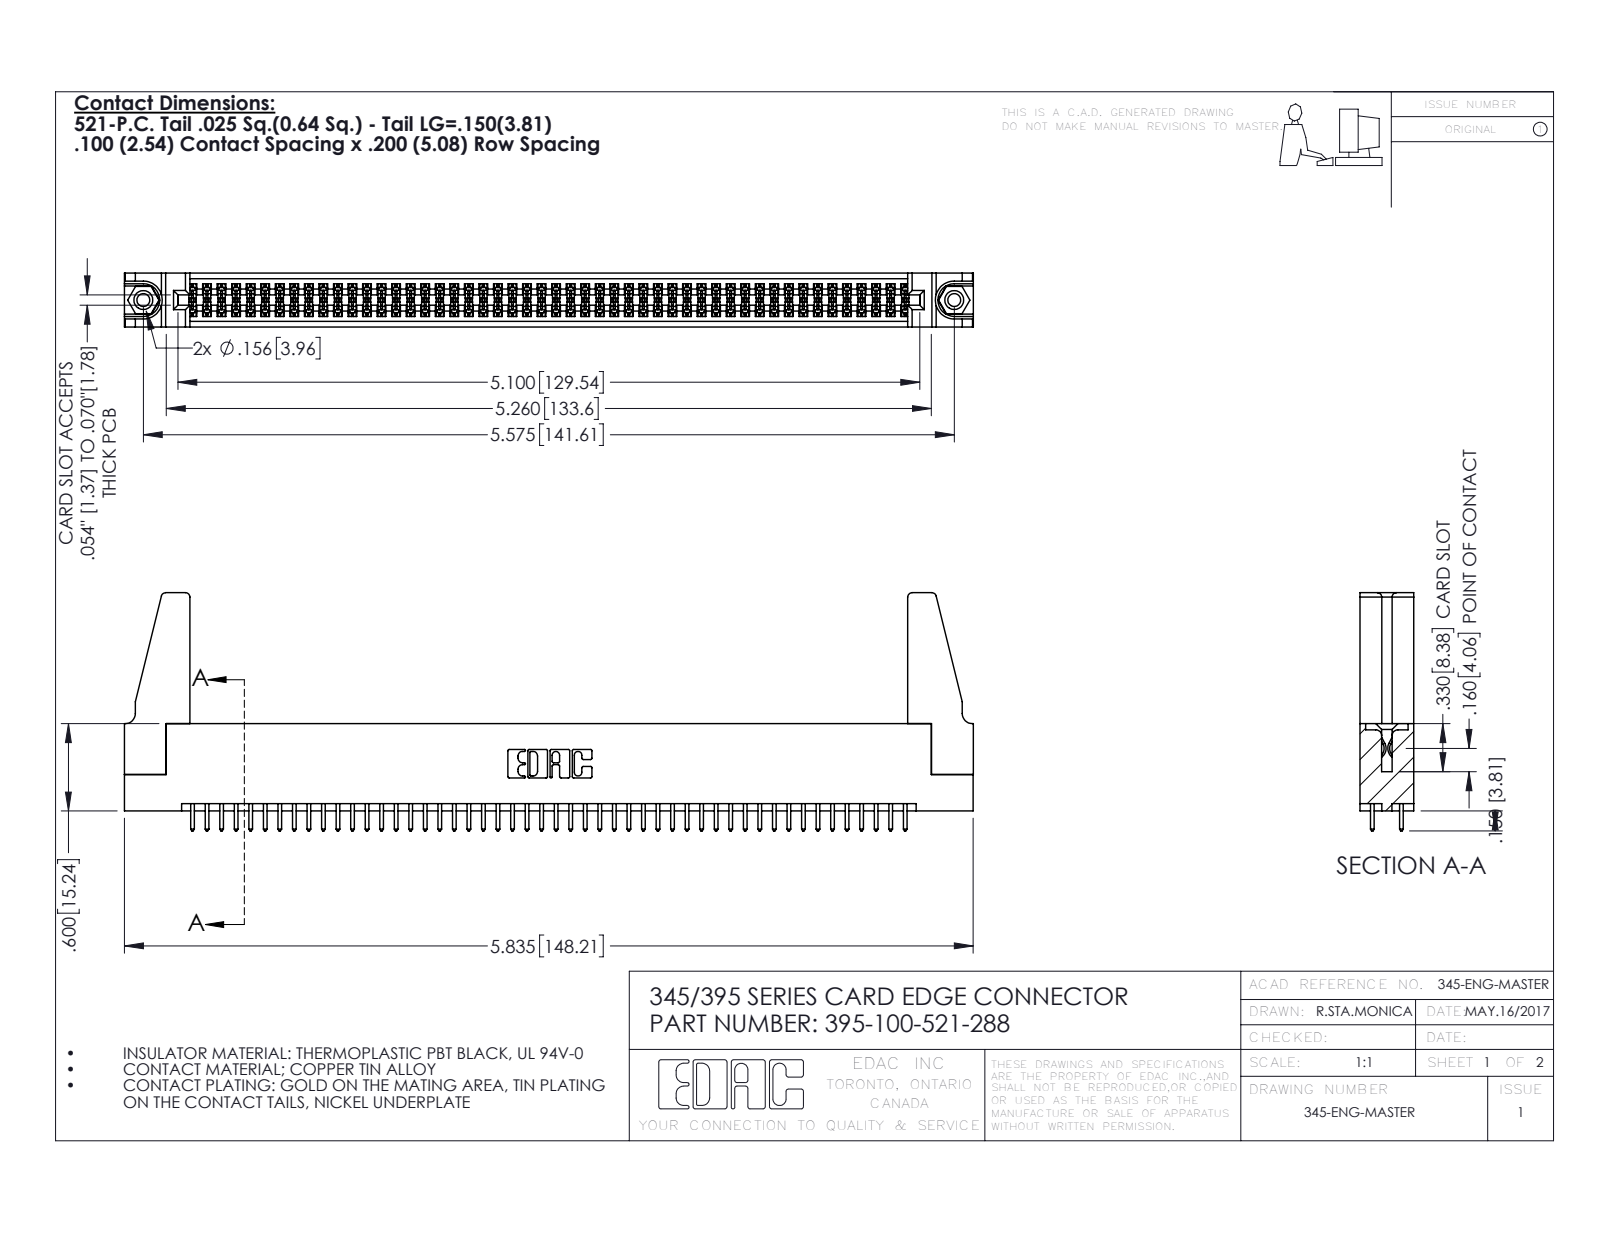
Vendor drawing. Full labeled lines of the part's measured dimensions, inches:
Part name (STEP PRODUCT): 345-220-078_345-220-088; 345 Part_Flush Mounting Lugs - 0.156 Dia-TH; 395-100-521-288; 345-250-001_345-250-001-102 (+1 more)
STEP written by: SolidWorks 2016 (CONFIG_CONTROL_DESIGN)
Units: inches
Bodies: 105 solids, 5250 faces (3452 planar, 1782 cylindrical, 16 other)
Overall size (bounding box): 5.836 × 1.637 × 0.37
Volume: 1.079 in³ · Surface area: 37.74 in²
Round holes (diameter × count): ⌀0.089 ×2, ⌀0.125 ×2, ⌀0.156 ×2, ⌀0.064 ×1
Round bosses / shafts (diameter × count): ⌀0.155 ×2
Partial cylindrical surfaces — rounded edges, fillets, slot ends (radius × count): R0.006 ×150, R0.01 ×100, R0.01 ×22, R0.03 ×8, R0.007 ×6, R0.031 ×6, R0.026 ×3, R0.014 ×2
Main face-to-face distances: 0.072, 0.298, 0.37, 0.2, 0.098, 0.272, 0.025, 0.225, 0.175, 0.149
Hole centre spacings: 0.27, 5.339, 5.575
